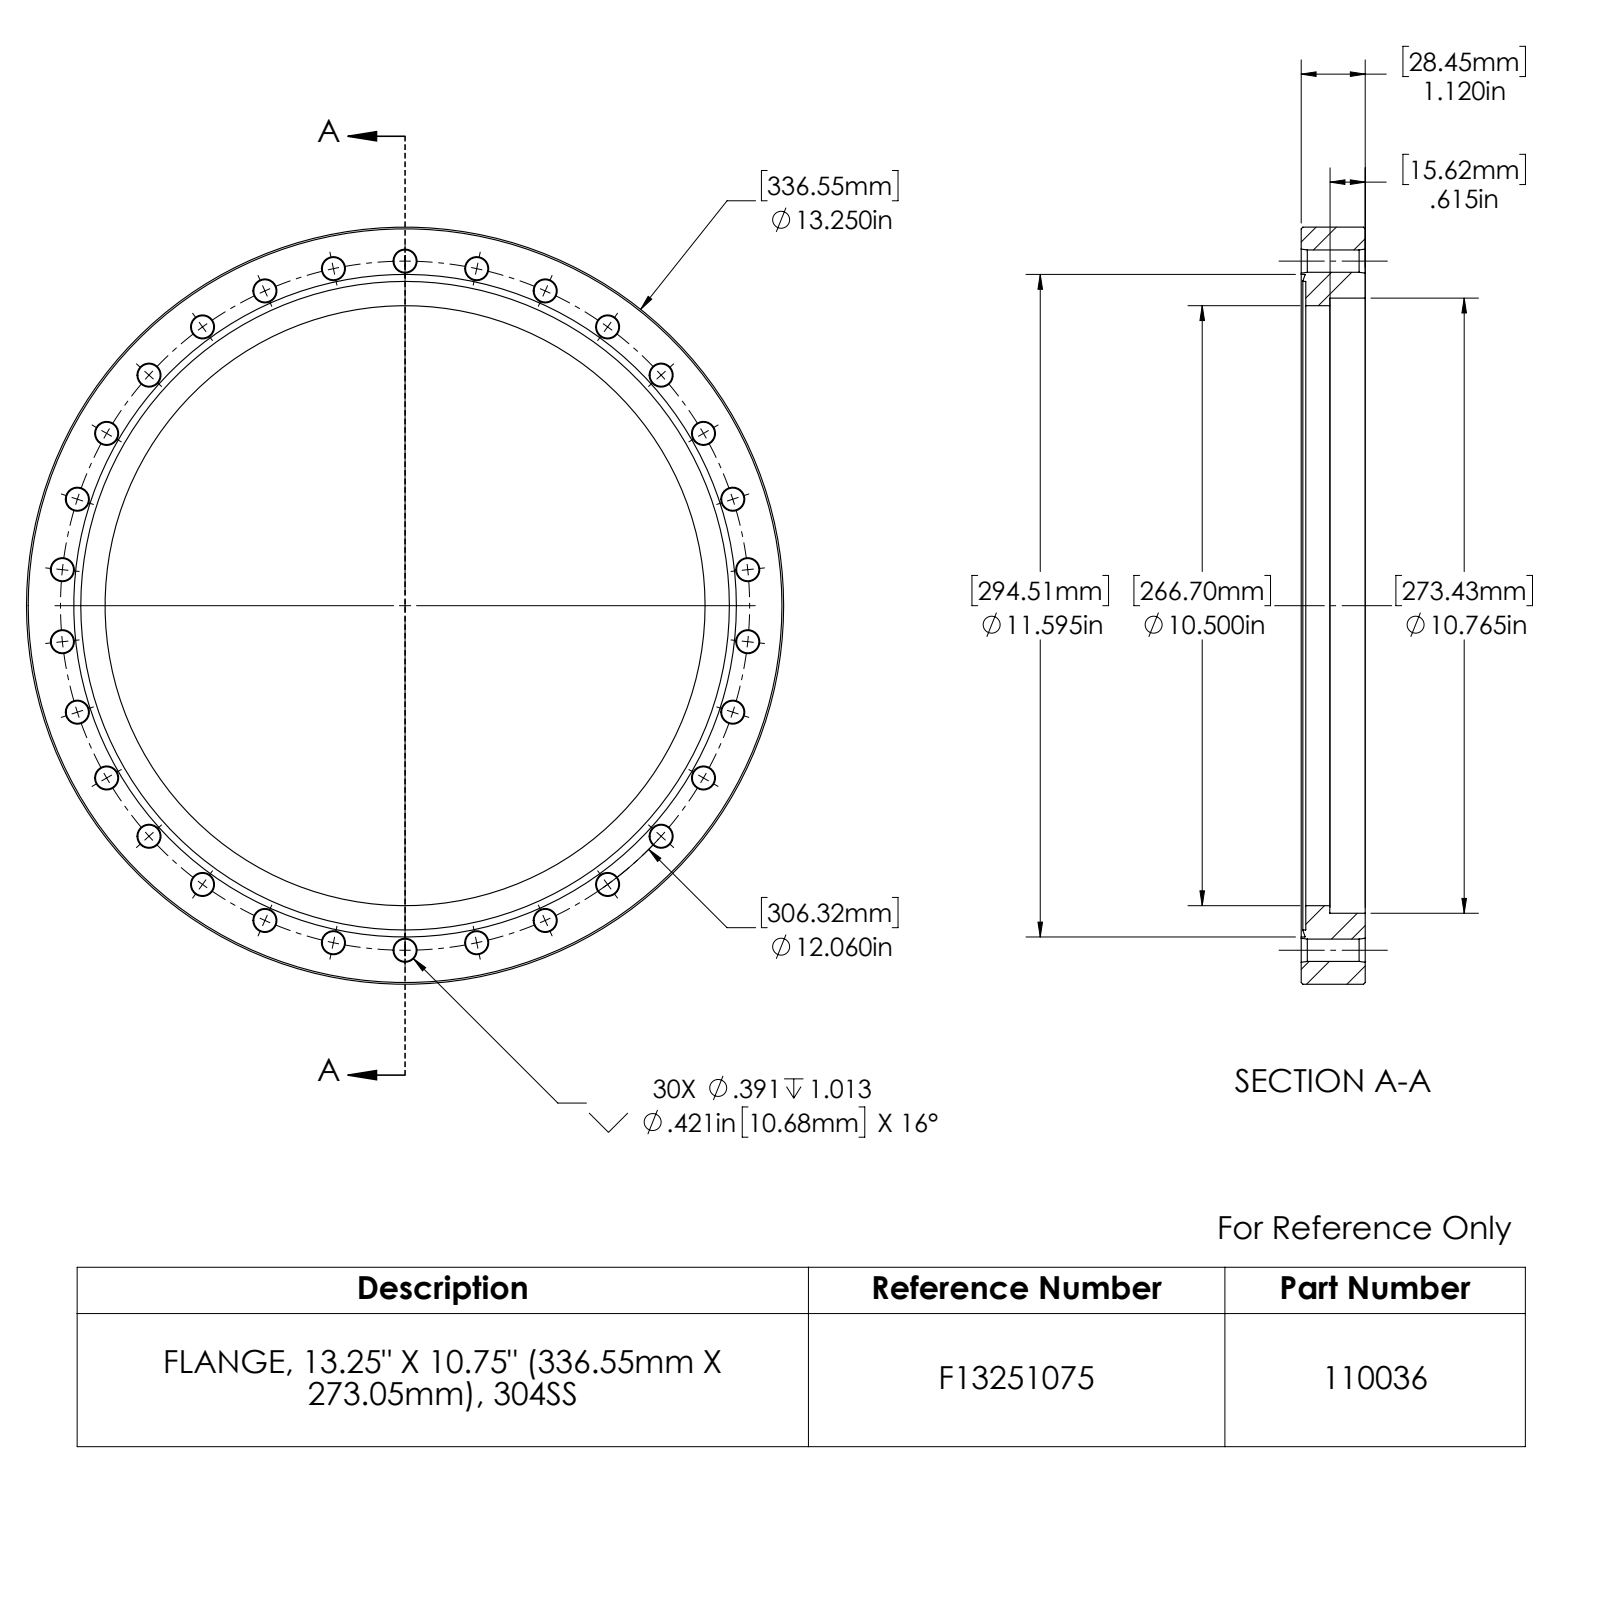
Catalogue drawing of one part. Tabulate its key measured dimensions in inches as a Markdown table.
| quantity | value |
| --- | --- |
| part name | 110036_A |
| STEP written by | SolidWorks 2022 (CONFIG_CONTROL_DESIGN) |
| units | inches |
| bodies | 1 solid, 208 faces (4 planar, 70 cylindrical, 134 other) |
| overall size | 13.25 × 13.25 × 1.12 |
| volume | 49.2 in³ |
| surface area | 220.1 in² |
| round holes (diameter × count) | 0.391 × 30, 10.5 × 1, 10.765 × 1, 11.35 × 1, 11.595 × 1 |
| round bosses / shafts (diameter × count) | 13.25 × 1 |
| main face-to-face distances | 1.12, 0.08, 1.04, 0.5, 0.42, 0.62 |
| hole center spacings | 3.727, 11.994, 8.07, 11.796, 9.757, 11.017, 4.905, 7.089 |
